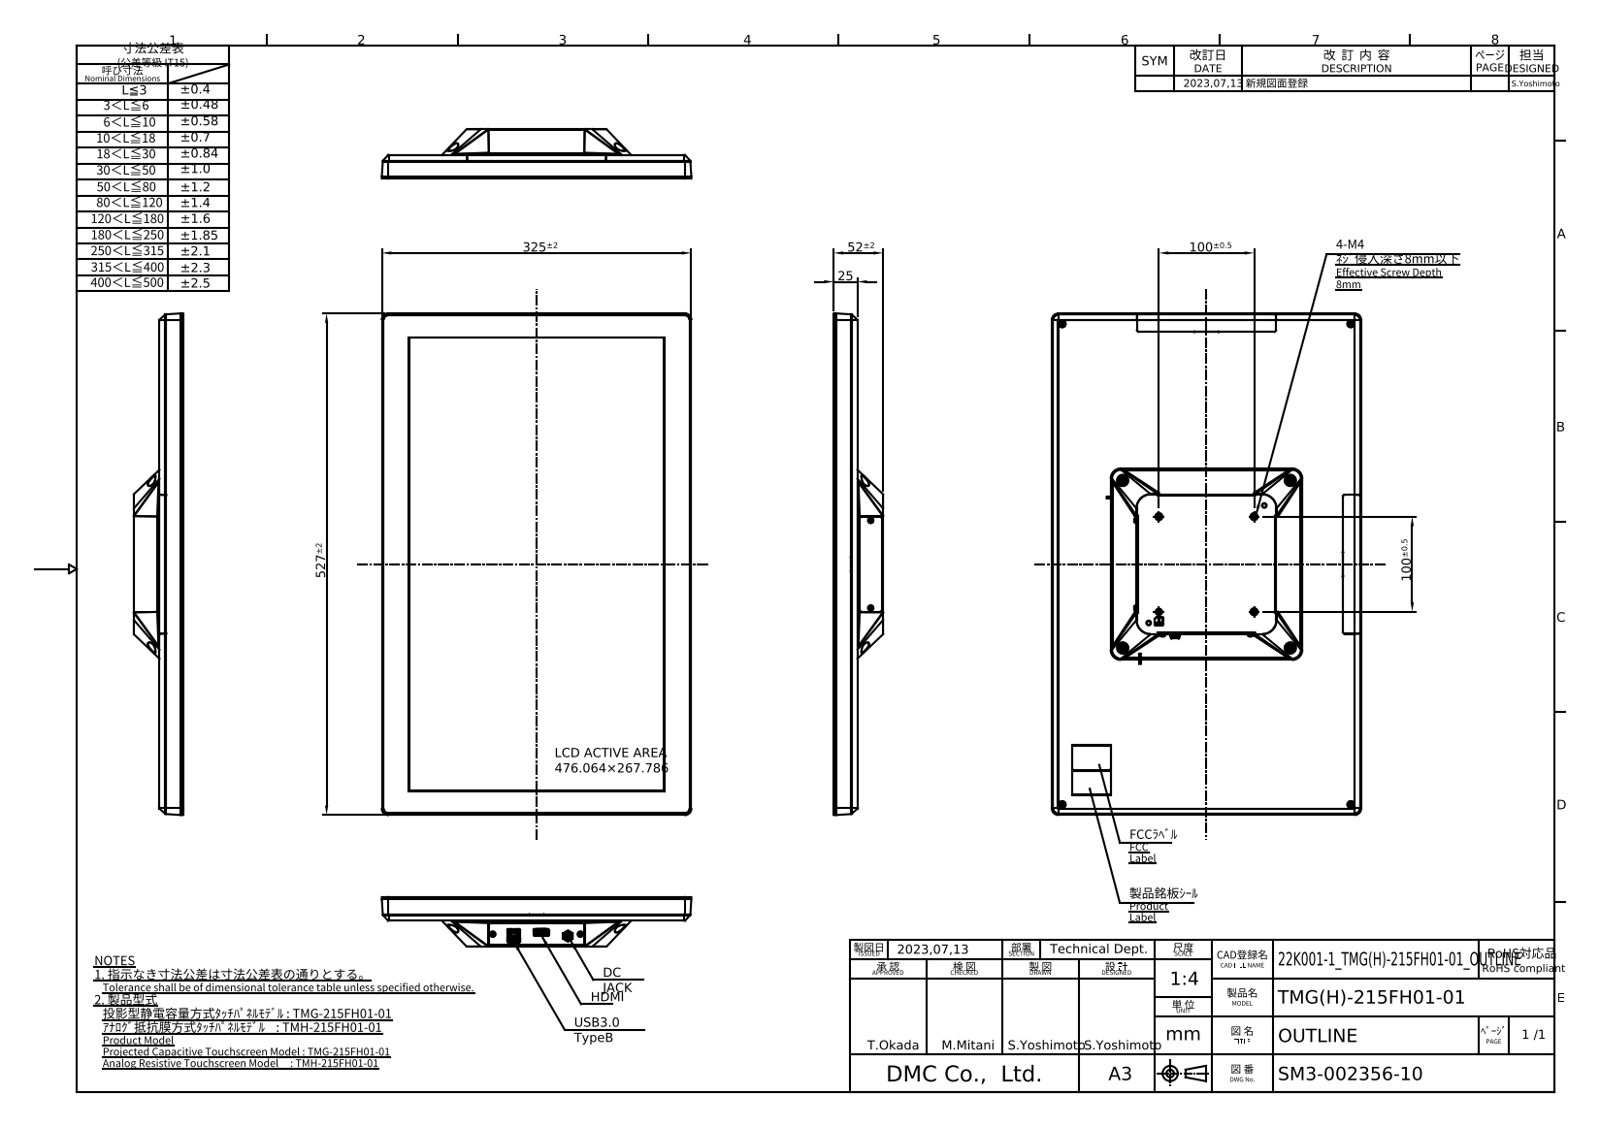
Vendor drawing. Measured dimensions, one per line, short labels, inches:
name: TMG(H)-215FH01-01_HP用
written by: Autodesk Inventor 2020 (AUTOMOTIVE_DESIGN)
unit: in
bodies: 1 solid, 8040 faces (5640 planar, 1317 cylindrical, 1083 other)
size: 20.748 × 12.795 × 2.047
volume: 66.7 in³; area: 1 438 in²
holes: 22× ⌀0.102, 10× ⌀0.197, 8× ⌀0.128, 8× ⌀0.138, 8× ⌀0.157, 7× ⌀0.181, 7× ⌀0.22, 5× ⌀0.26, 4× ⌀0.146, 4× ⌀0.15, 4× ⌀0.177, 4× ⌀0.315
bosses: 16× ⌀0.118, 10× ⌀0.142, 9× ⌀0.236, 8× ⌀0.248, 8× ⌀0.217, 8× ⌀0.098, 6× ⌀0.181, 5× ⌀0.315
rounds: 117× R0.012, 89× R0.02, 87× R0.008, 87× R0.039, 81× R0.004, 59× R0.006, 44× R0.079, 24× R0.024
face distances: 0.098, 0.874, 0.972, 0.776, 1.063, 1.937, 0.787, 0.02, 1.85, 0.087
hole spacings: 10.176, 3.285, 3.392, 4.134, 6.541, 6.676, 7.817, 9.195
